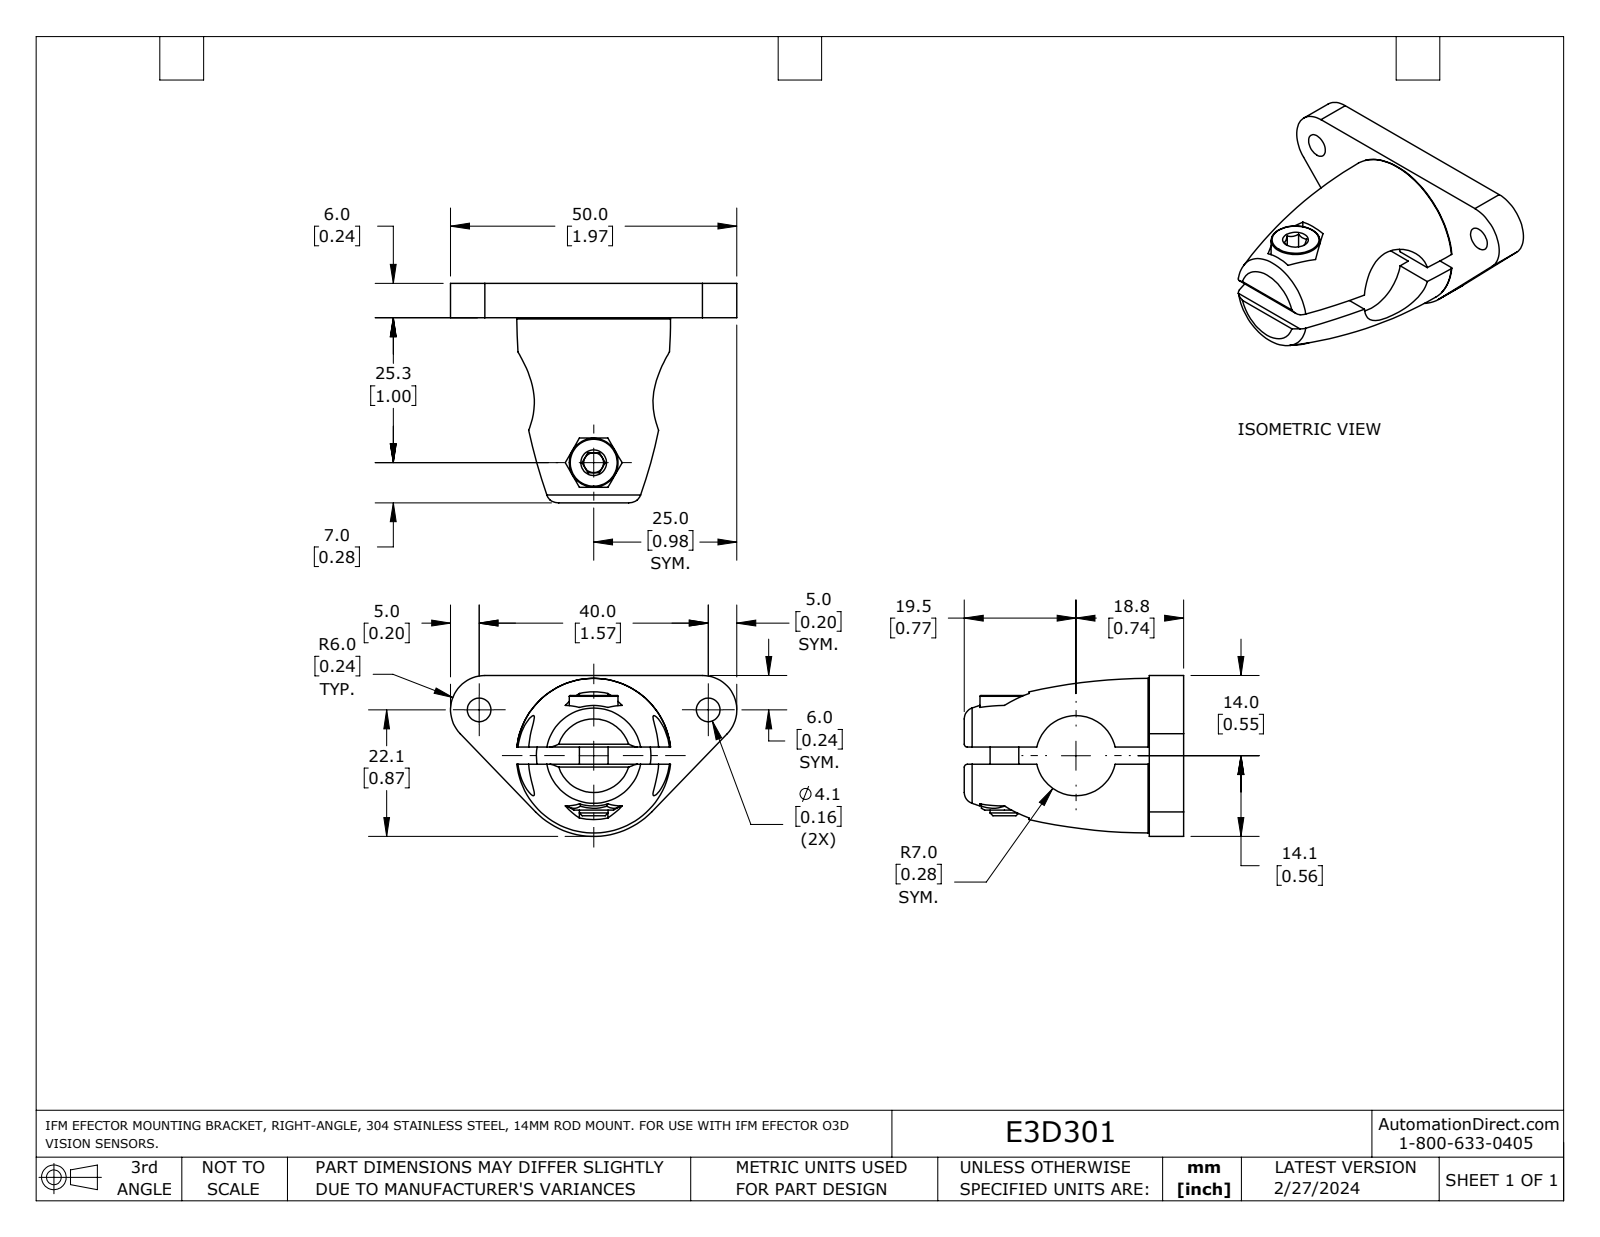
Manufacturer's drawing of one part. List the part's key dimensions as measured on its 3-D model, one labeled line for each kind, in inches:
Part name (STEP PRODUCT): E3D301
STEP written by: SolidWorks 2023 (AUTOMOTIVE_DESIGN)
Units: inches
Bodies: 5 solids, 119 faces (64 planar, 34 cylindrical, 21 other)
Overall size (bounding box): 1.969 × 1.508 × 1.106
Volume: 0.77 in³ · Surface area: 13.4 in²
Round holes (diameter × count): ⌀0.163 ×3, ⌀0.217 ×1, ⌀0.551 ×1, ⌀0.709 ×1, ⌀0.945 ×1
Round bosses / shafts (diameter × count): ⌀0.787 ×1, ⌀0.335 ×1, ⌀0.197 ×1
Partial cylindrical surfaces — rounded edges, fillets, slot ends (radius × count): R0.157 ×8, R0.02 ×4, R0.236 ×2, R0.433 ×1, R0.555 ×1
Main face-to-face distances: 0.118, 0.236, 0.059, 0.177, 0.492, 0.61, 0.157, 0.276, 0.339, 1.272
Hole centre spacings: 0.848, 1.575
